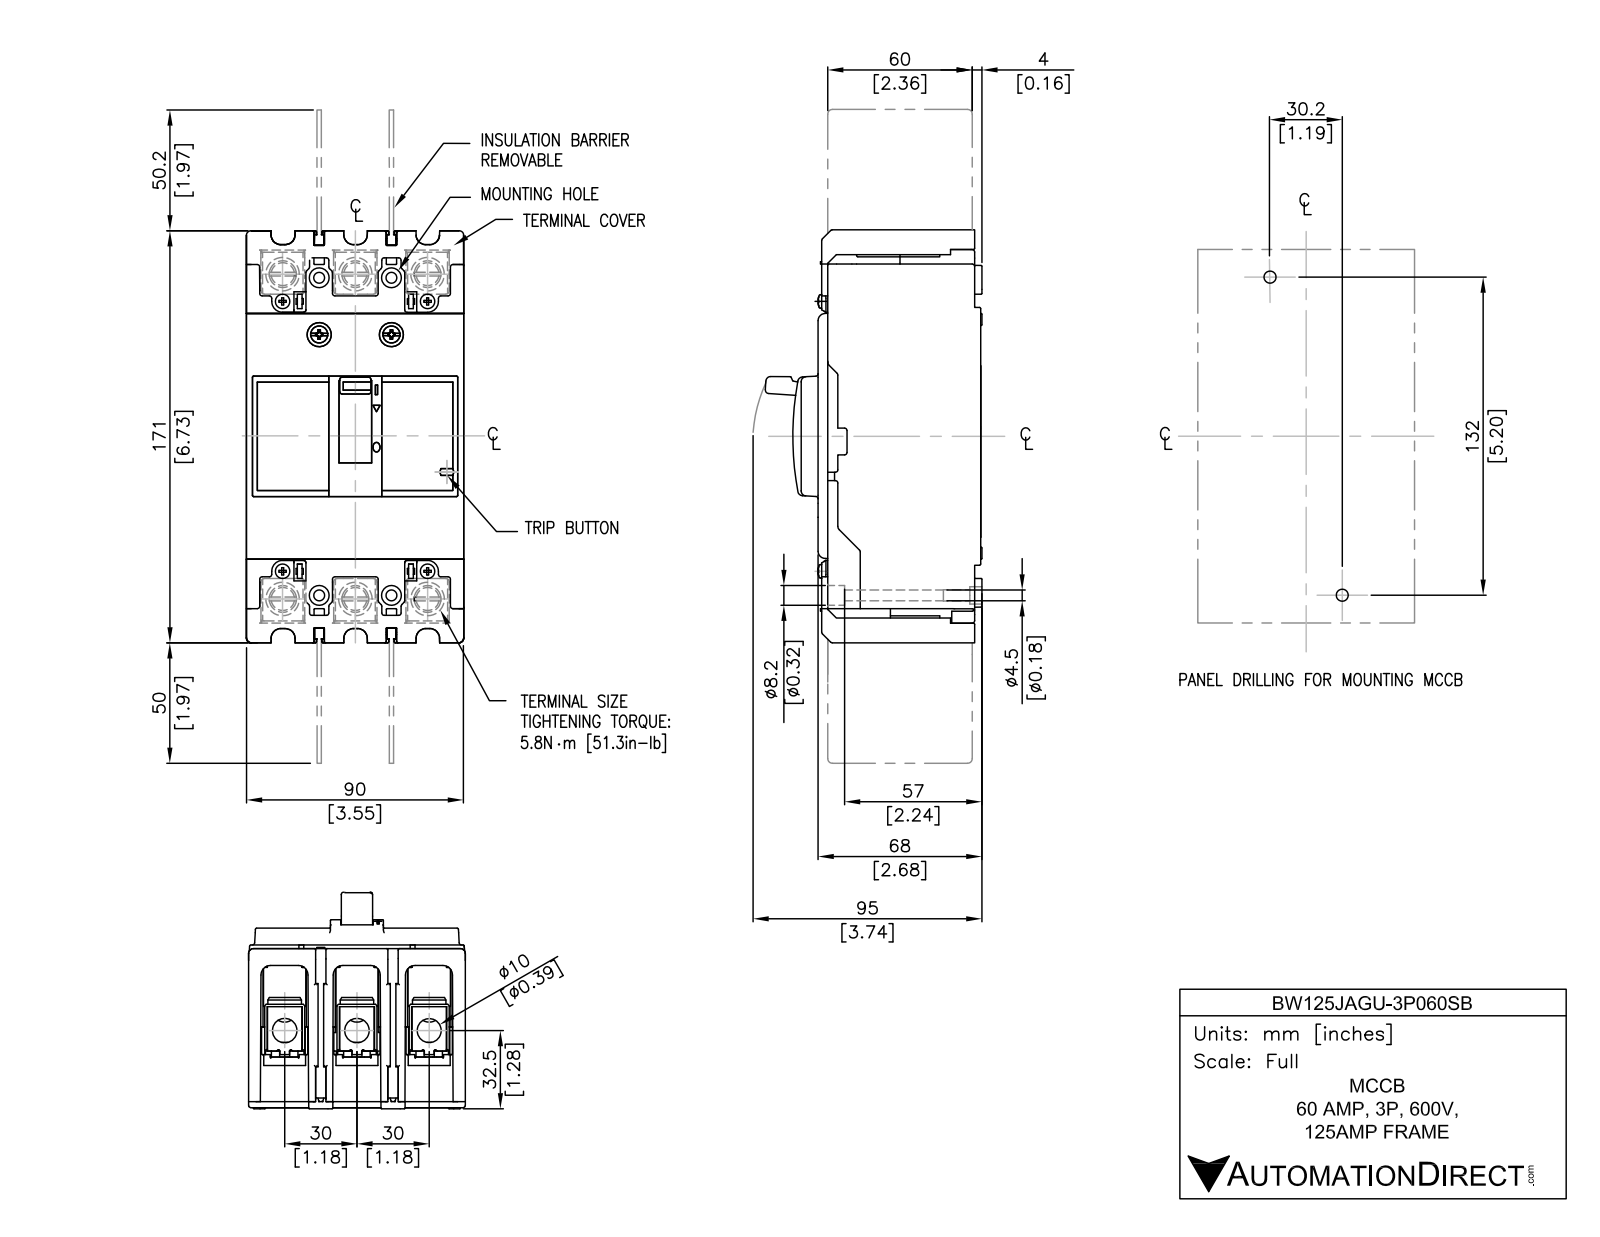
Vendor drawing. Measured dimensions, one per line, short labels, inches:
name: BW125JAGU-3P060SB
written by: SolidWorks 2018 (AUTOMOTIVE_DESIGN)
unit: in
bodies: 14 solids, 452 faces (340 planar, 88 cylindrical, 24 other)
size: 10.197 × 3.602 × 3.543
volume: 57.4 in³; area: 230.3 in²
holes: 6× ⌀0.315, 4× ⌀0.177, 4× ⌀0.323
bosses: 6× ⌀0.472
rounds: 12× R0.157, 6× R0.079, 6× R0.118
face distances: 1.181, 1.11, 1.252, 2.291, 2.433, 0.142, 3.543, 0.236, 2.402, 1.039
hole spacings: 0.593, 5.289, 1.181, 1.772, 5.444, 5.546, 5.315, 2.362
